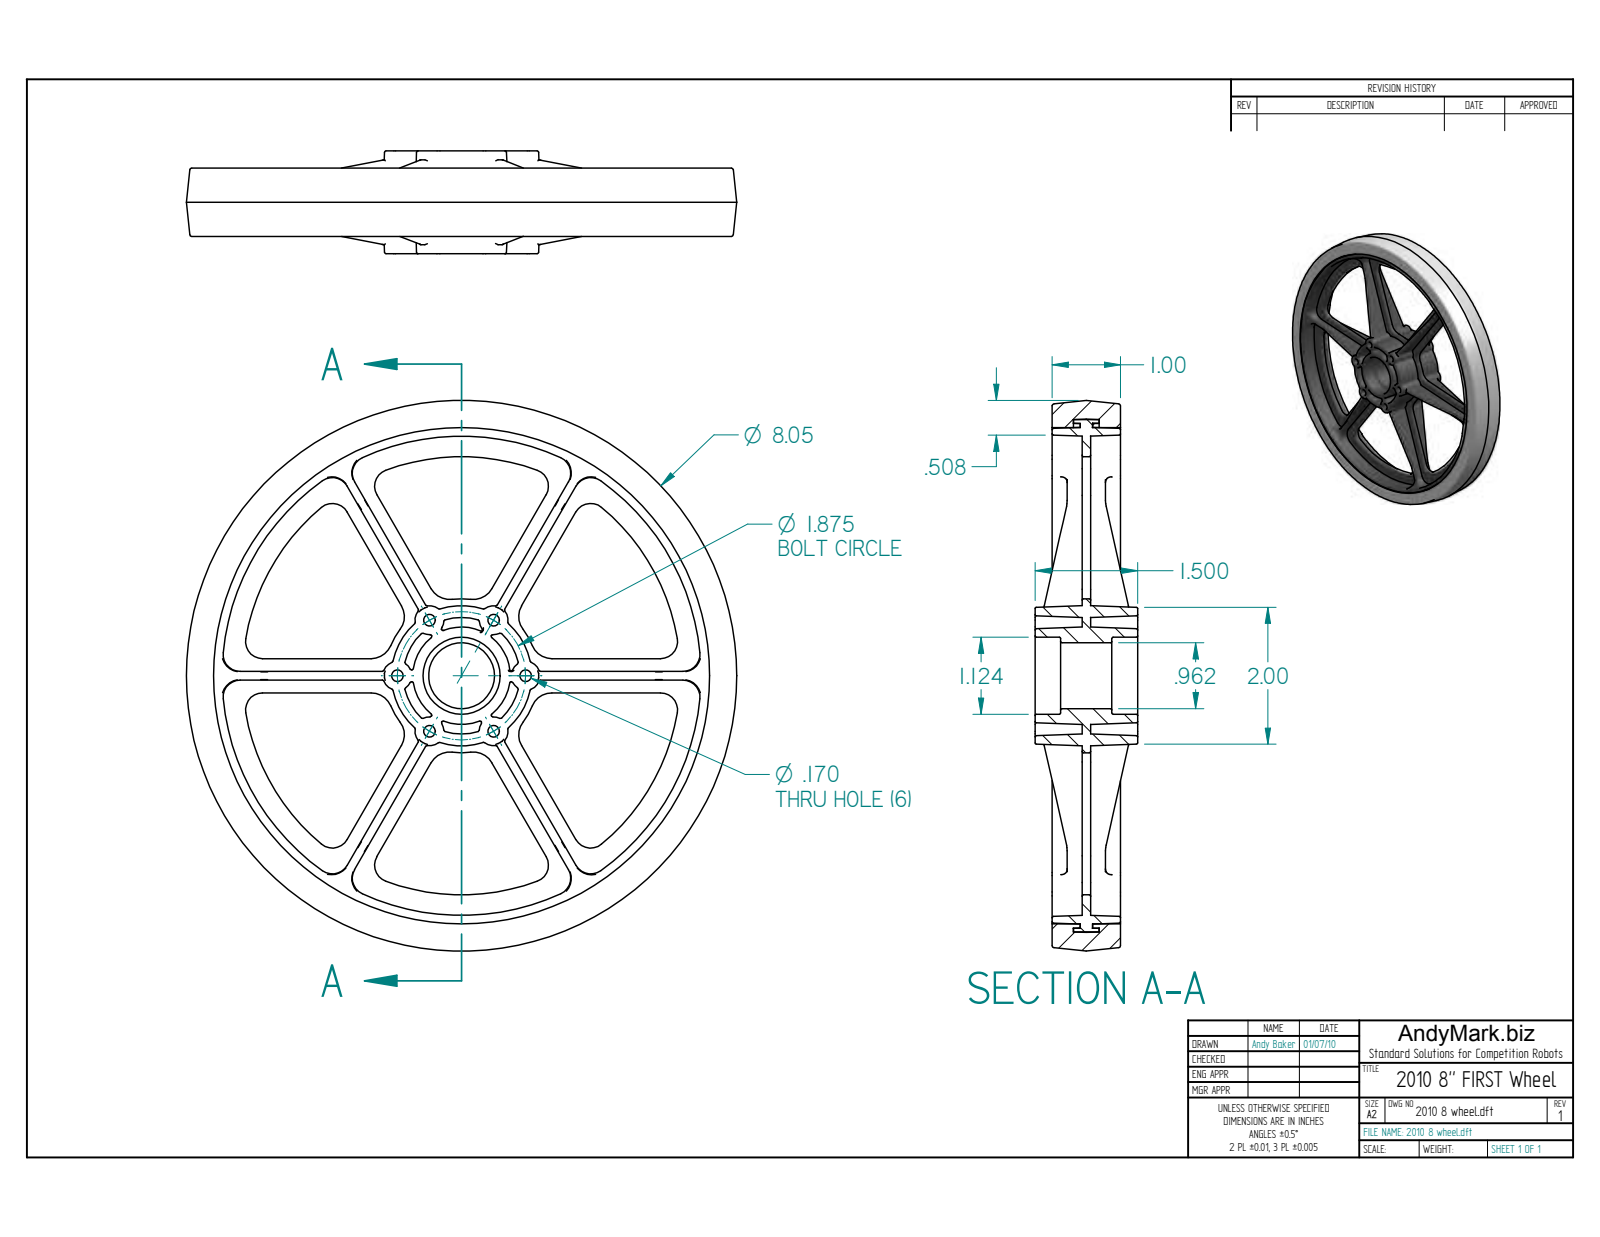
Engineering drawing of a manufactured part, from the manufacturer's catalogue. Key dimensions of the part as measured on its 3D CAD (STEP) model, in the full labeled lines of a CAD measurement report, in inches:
Part name (STEP PRODUCT): 2010 8 tread; 2010 8 hub
STEP written by: Unknown (CONFIG_CONTROL_DESIGN)
Units: inches
Bodies: 4 solids, 1922 faces (224 planar, 248 cylindrical, 1450 other)
Overall size (bounding box): 8.045 × 8.045 × 1.75
Volume: 34.49 in³ · Surface area: 445.7 in²
Round holes (diameter × count): ⌀0.17 ×6, ⌀0.962 ×1, ⌀1.124 ×1, ⌀7.25 ×1, ⌀7.376 ×1, ⌀7.484 ×1
Round bosses / shafts (diameter × count): ⌀7.374 ×1
Partial cylindrical surfaces — rounded edges, fillets, slot ends (radius × count): R0.02 ×39, R0.25 ×12, R0.313 ×12, R1.125 ×1, R3.2 ×1
Main face-to-face distances: 0.5, 0.124, 0.438, 0.562, 1, 0.062, 0.41, 0.59, 0.09, 0.313
Hole centre spacings: 0.937, 1.624, 1.875, 0.938
